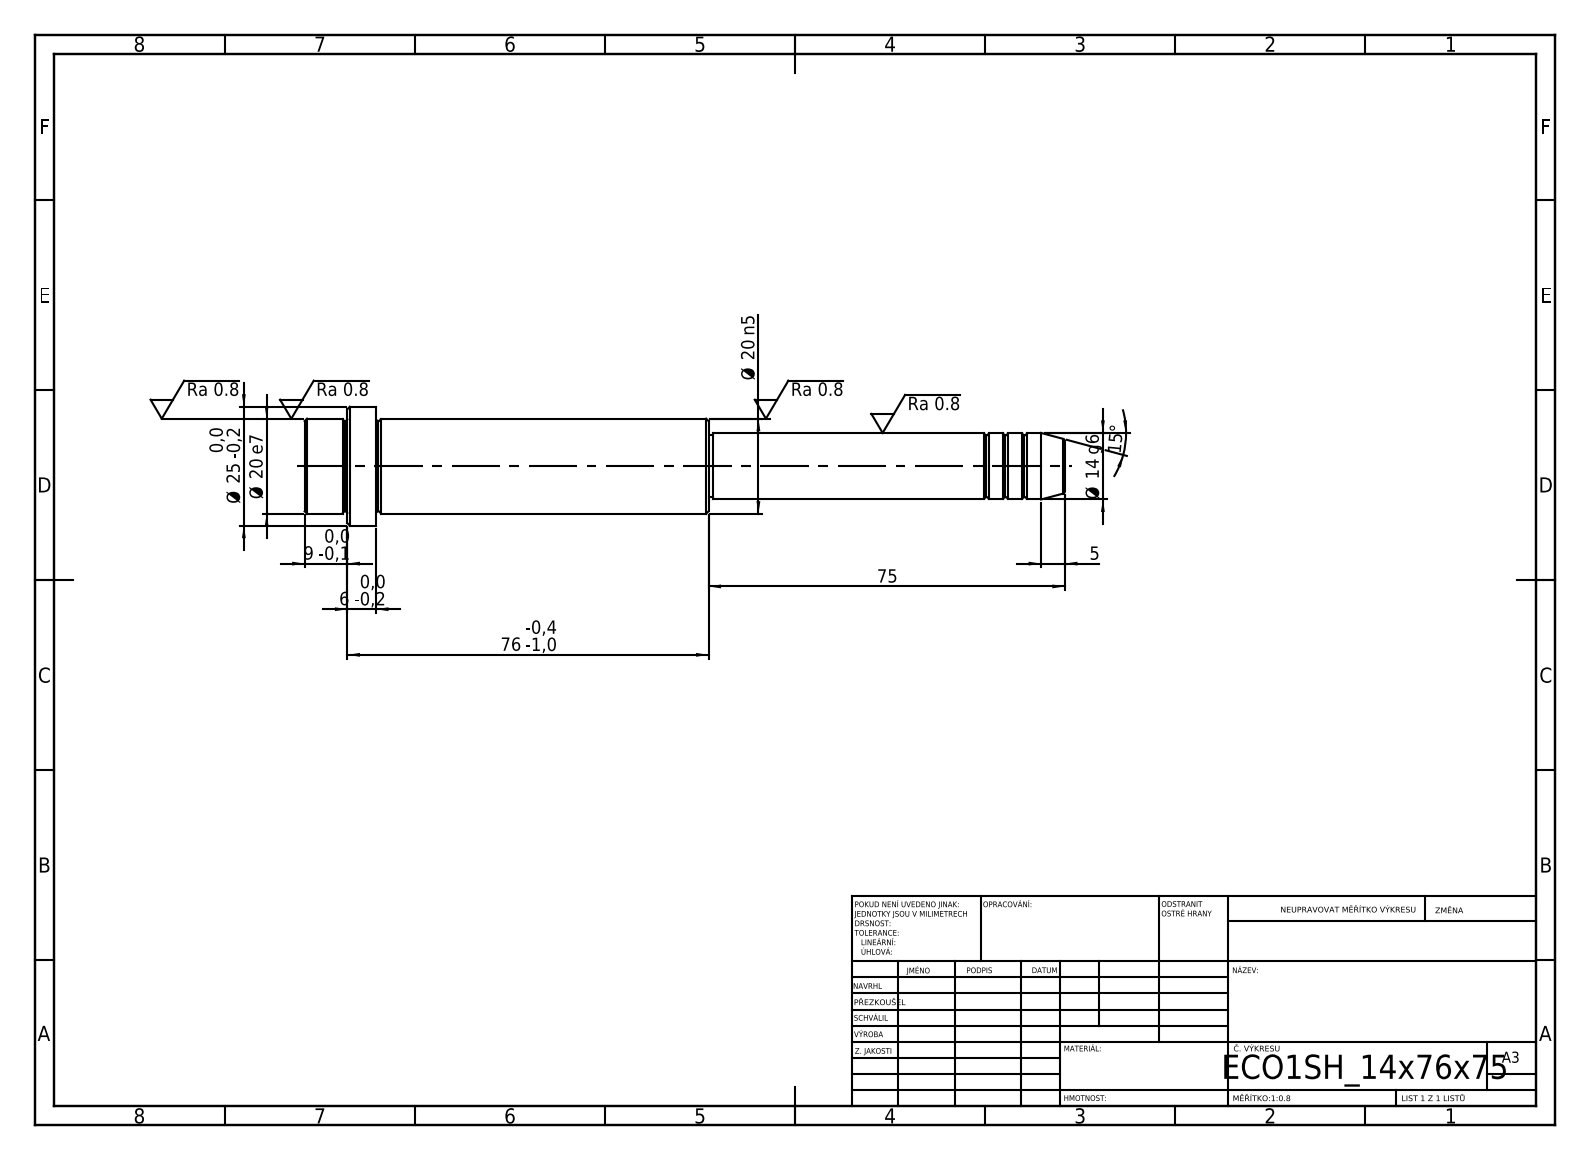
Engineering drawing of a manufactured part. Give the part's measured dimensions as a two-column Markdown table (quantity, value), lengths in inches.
| quantity | value |
| --- | --- |
| STEP written by | SolidWorks 2019 (CONFIG_CONTROL_DESIGN) |
| units | inches |
| bodies | 1 solid, 52 faces (6 planar, 16 cylindrical, 30 other) |
| overall size | 6.299 × 0.984 × 0.984 |
| volume | 2.381 in³ |
| surface area | 15.12 in² |
| round bosses / shafts (diameter × count) | 0.984 × 1, 0.787 × 1, 0.551 × 1, 0.512 × 1 |
| main face-to-face distances | 0.591, 2.756, 3.346, 2.992, 0.236, 0.354, 2.953, 5.709, 5.945, 6.299 |
